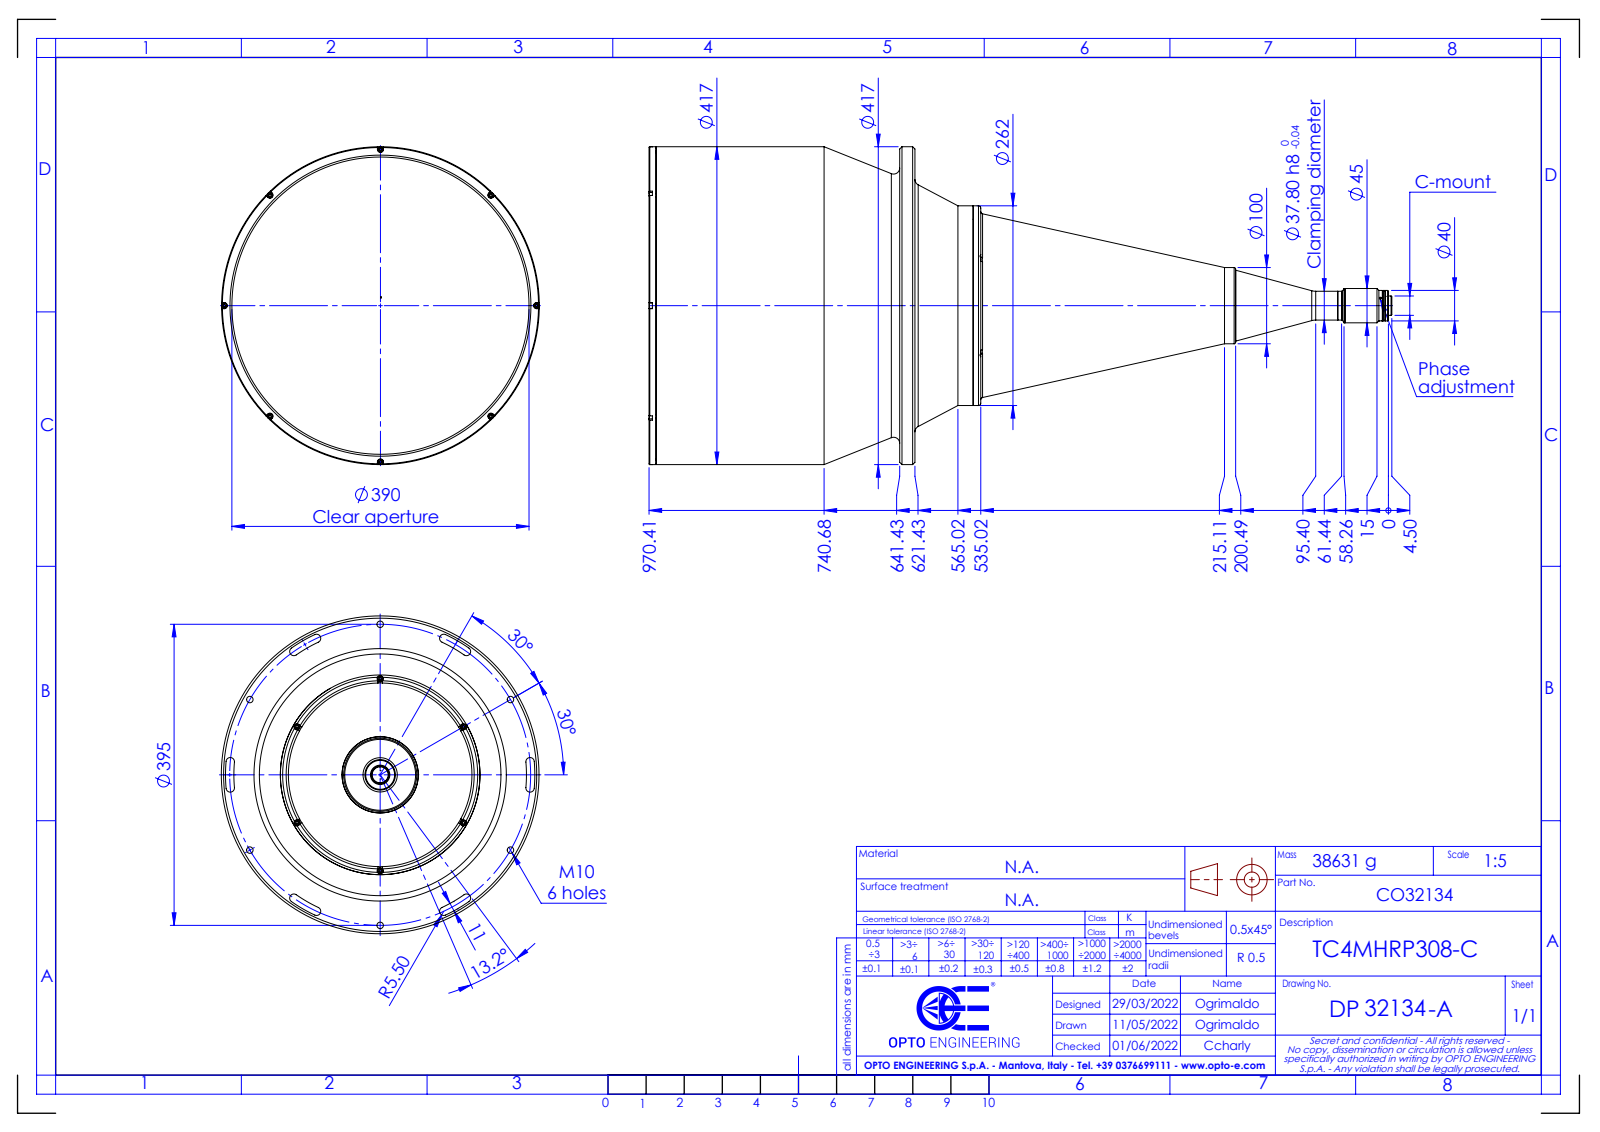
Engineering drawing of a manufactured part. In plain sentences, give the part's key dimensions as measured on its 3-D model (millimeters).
The part is named "DP32134-A_TC4MHRP308-C". Its 3-D file was written by "SolidWorks 2021 (CONFIG_CONTROL_DESIGN)". It is 0 solids with 277 faces: 61 planar, 127 cylindrical and 89 other. Overall it measures 974.91 by 417 by 417 millimeters. Round holes: 6 of diameter 8, 6 of diameter 8.5, 3 of diameter 2.5, 1 of diameter 22.5, 1 of diameter 390. Round bosses or shafts: 12 of diameter 7, 1 of diameter 417, 1 of diameter 262, 1 of diameter 100, 1 of diameter 93, 1 of diameter 45, 1 of diameter 40, 1 of diameter 37.8. Partial cylindrical surfaces (rounded edges, fillets, slot ends): 12 of radius 5.5, 4 of radius 4, 1 of radius 192, 1 of radius 203. The main face-to-face distances are 20, 96.41, 76.41, 328.98, 348.98, 425.39, 8.7, 320.28, 340.28, 416.69. The hole center spacings are 126, 173.2, 197.5, 282.43, 71.5, 218.24, 323.5, 342.08.
